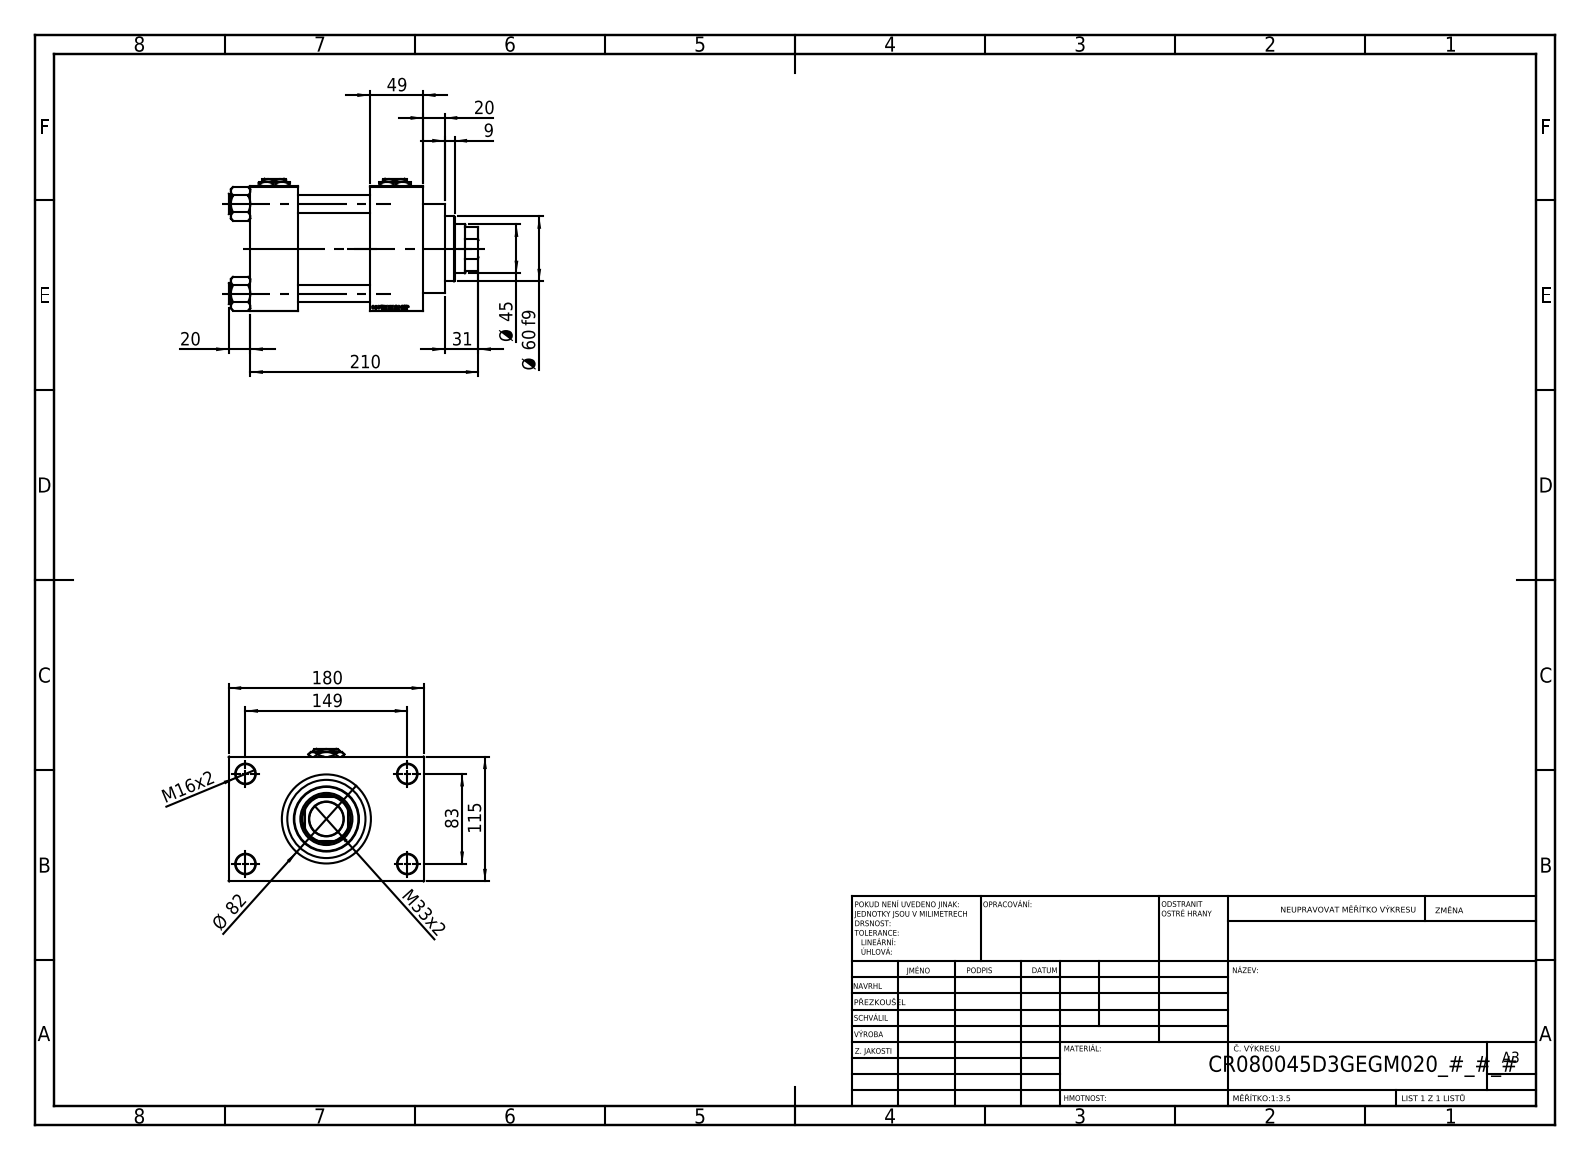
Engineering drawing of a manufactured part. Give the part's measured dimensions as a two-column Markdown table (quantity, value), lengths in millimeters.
| quantity | value |
| --- | --- |
| part name | Zatka_pro_OIL_PORT; V215_VC_A; NUT_M5_D; V215CR_VCP_D (+2 more) |
| STEP written by | SolidWorks 2019 (CONFIG_CONTROL_DESIGN) |
| units | millimeters |
| bodies | 13 solids, 1253 faces (593 planar, 100 cylindrical, 560 other) |
| overall size | 230 × 180 × 122 |
| volume | 2 008 000 mm³ |
| surface area | 306 468 mm² |
| round holes (diameter × count) | 16 × 4, 18 × 4, 7 × 2, 26.44 × 2, 35 × 2, 31.5 × 1, 45 × 1, 48 × 1, 61 × 1, 72 × 1, 80 × 1 |
| round bosses / shafts (diameter × count) | 19 × 4, 86 × 1, 82 × 1, 60 × 1 |
| partial cylindrical surfaces (radius × count) | 22 × 1 |
| main face-to-face distances | 115, 110, 66, 49, 44, 159, 147.5, 32.5, 20, 69 |
| hole center spacings | 33.15, 58.48, 82.7, 85.28, 89.24, 115.85, 142.43, 83 |
